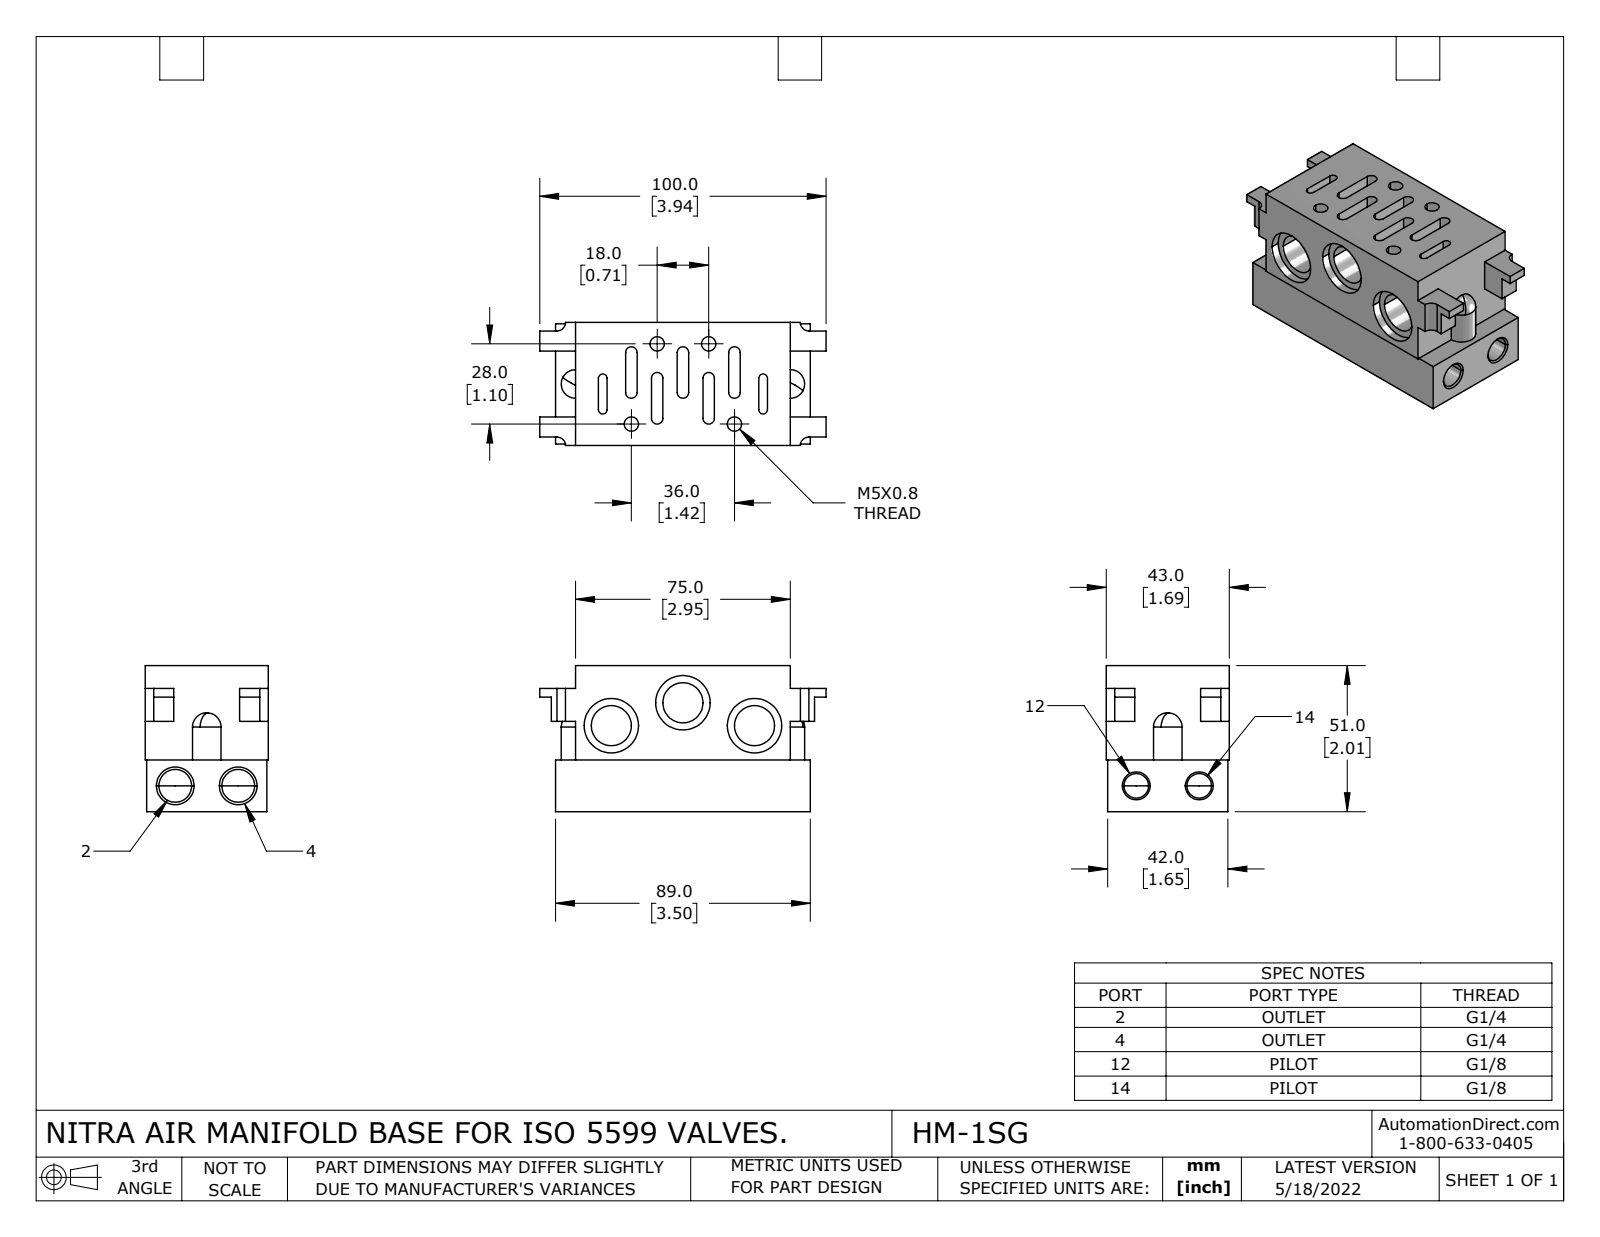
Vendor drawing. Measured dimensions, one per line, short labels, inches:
name: HM-1SG
written by: SolidWorks 2021 (CONFIG_CONTROL_DESIGN)
unit: in
bodies: 1 solid, 138 faces (70 planar, 48 cylindrical, 20 other)
size: 3.937 × 2.008 × 1.693
volume: 9.187 in³; area: 46.67 in²
holes: 4× ⌀0.197, 3× ⌀0.551, 3× ⌀0.748, 2× ⌀0.337, 2× ⌀0.451
rounds: 10× R0.079, 4× R0.059, 4× R0.118, 2× R0.197
face distances: 1.673, 0.02, 2.008, 1.693, 1.654, 0.276, 0.118, 0.709, 3.228, 2.953
hole spacings: 1.033, 1.158, 1.531, 0.709, 0.866, 1.417, 1.969
